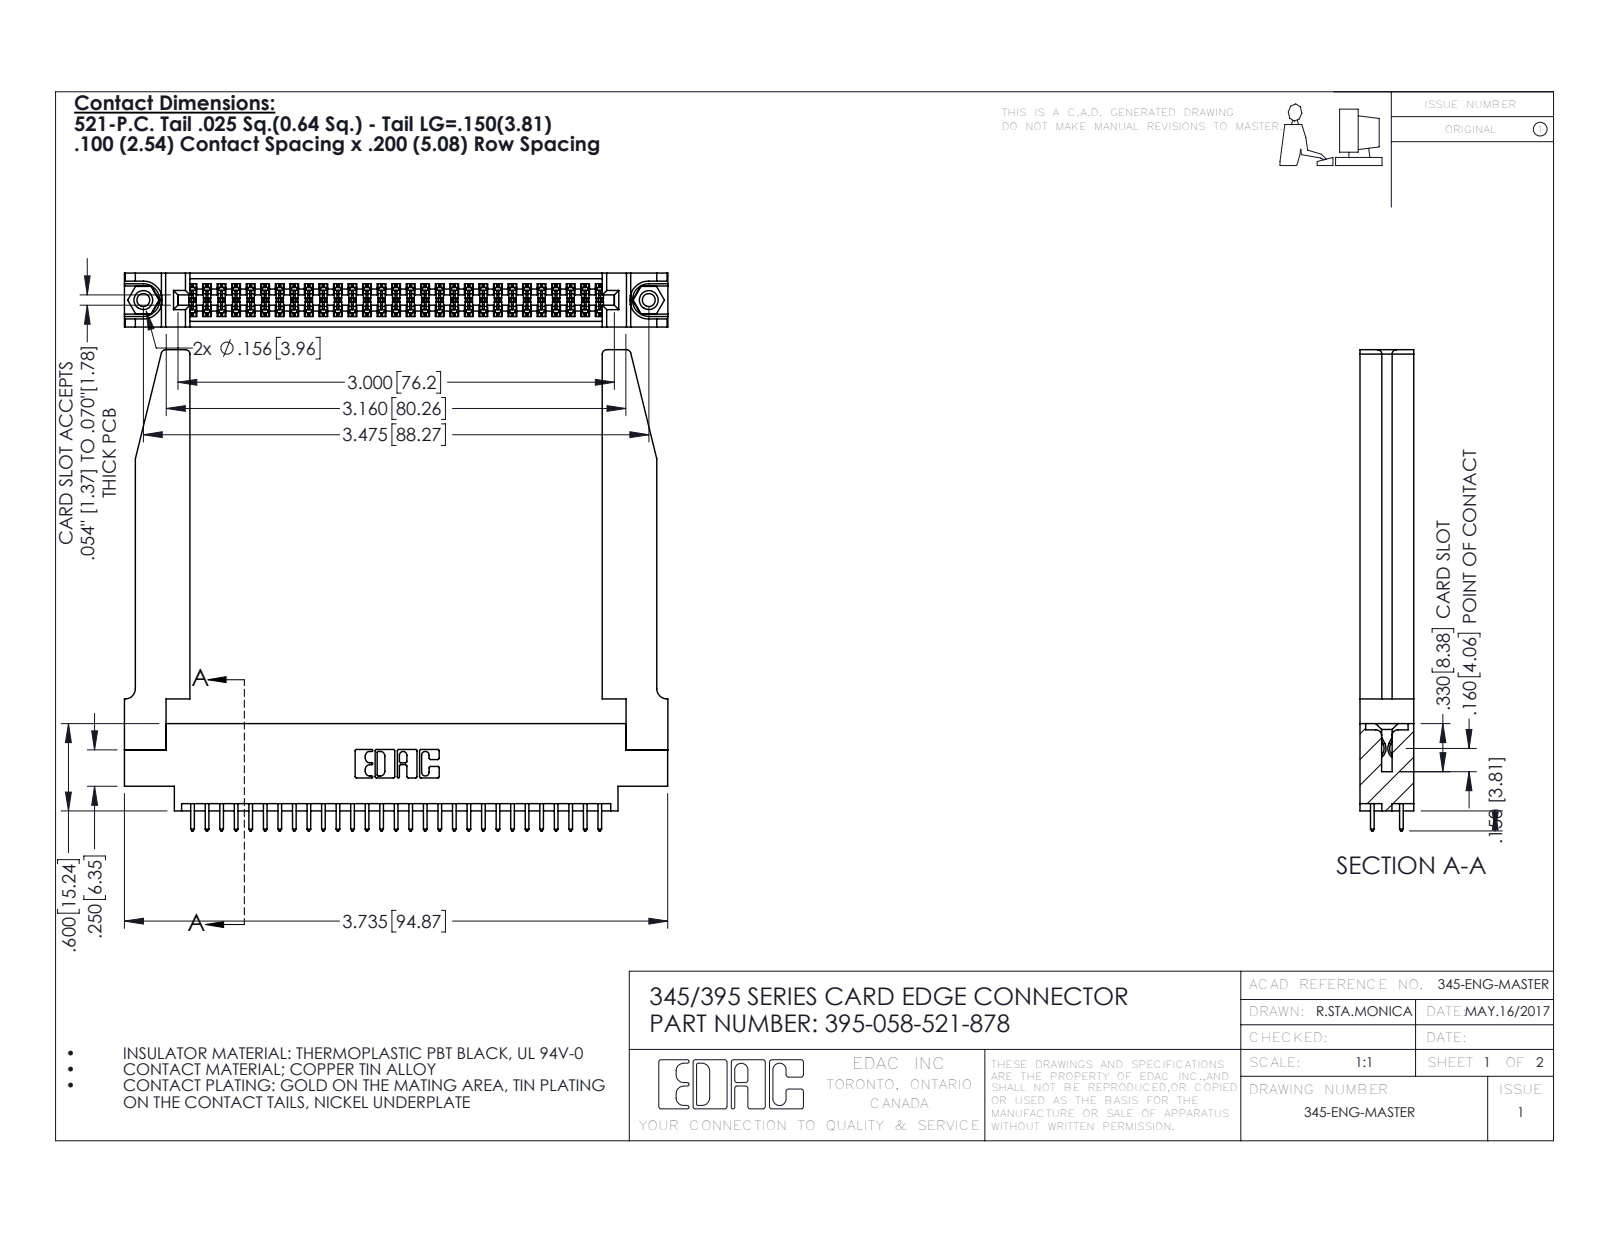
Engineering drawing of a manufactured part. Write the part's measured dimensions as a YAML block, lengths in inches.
part_name: "345-220-078_345-220-078; 395-058-521-878; 345-250-001_345-250-001-102; 345-292-001_345-293-121 (+1 more)"
step_written_by: "SolidWorks 2016 (CONFIG_CONTROL_DESIGN)"
units: inches
bodies: {solids: 63, faces: 3264, planar: 2140, cylindrical: 1072, other: 52}
overall_size: [3.736, 3.307, 0.37]
volume: 1.021
surface_area: 30.72
round_holes:
  - {diameter: 0.089, count: 2}
  - {diameter: 0.125, count: 2}
  - {diameter: 0.156, count: 2}
  - {diameter: 0.064, count: 1}
round_bosses_or_shafts:
  - {diameter: 0.155, count: 2}
partial_cylinders:
  - {radius: 0.006, count: 87}
  - {radius: 0.01, count: 58}
  - {radius: 0.01, count: 22}
  - {radius: 0.03, count: 8}
  - {radius: 0.007, count: 6}
  - {radius: 0.031, count: 6}
  - {radius: 0.026, count: 3}
  - {radius: 0.014, count: 2}
face_to_face_distances: [0.37, 0.072, 0.298, 0.098, 0.272, 0.025, 0.2, 0.225, 0.148, 0.15]
hole_center_spacings: [0.27, 3.24, 3.475]
